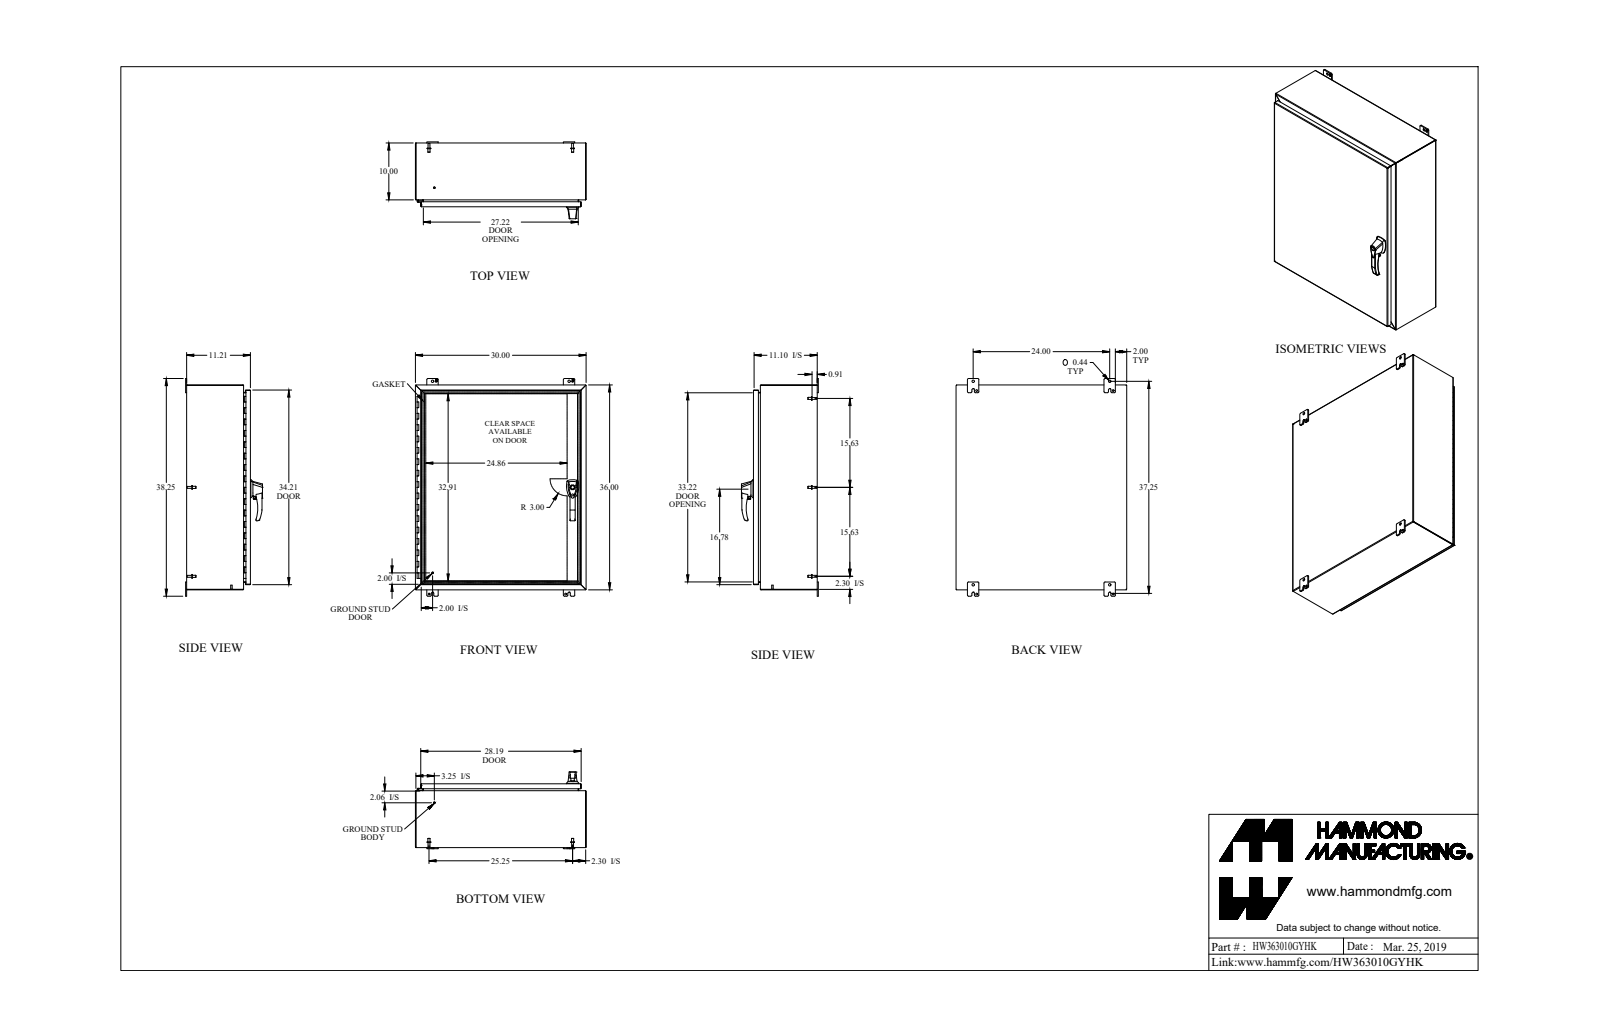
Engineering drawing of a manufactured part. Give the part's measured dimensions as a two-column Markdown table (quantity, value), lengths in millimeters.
| quantity | value |
| --- | --- |
| part name | HW363010GYHK |
| STEP written by | SolidWorks 2018 (AUTOMOTIVE_DESIGN) |
| units | millimeters |
| bodies | 46 solids, 1613 faces (789 planar, 651 cylindrical, 173 other) |
| overall size | 971.6 × 762 × 343.2 |
| volume | 5 396 000 mm³ |
| surface area | 5 607 000 mm² |
| round holes (diameter × count) | 4.5 × 6, 6.4 × 4, 8 × 4, 5 × 3, 6.7 × 3, 10.5 × 3, 6.5 × 2, 10 × 2, 11.1 × 2, 4.7 × 1, 5.9 × 1, 8.5 × 1 |
| round bosses / shafts (diameter × count) | 9.5 × 11, 16.5 × 6, 8.4 × 6, 6.4 × 6, 4 × 6, 25.4 × 3, 16 × 2, 13 × 2 |
| partial cylindrical surfaces (radius × count) | 4.8 × 34, 6.4 × 27, 0.9 × 20, 2.7 × 20, 1.5 × 12, 2.9 × 12, 3.2 × 9, 1.1 × 8 |
| main face-to-face distances | 1.8, 1.8, 282.9, 281.1, 284.7, 282.9, 760.2, 912.6, 758.3, 762 |
| hole center spacings | 358.6, 358.6, 717.2, 28.2, 246.3, 358.6, 609.6, 627.9 |
